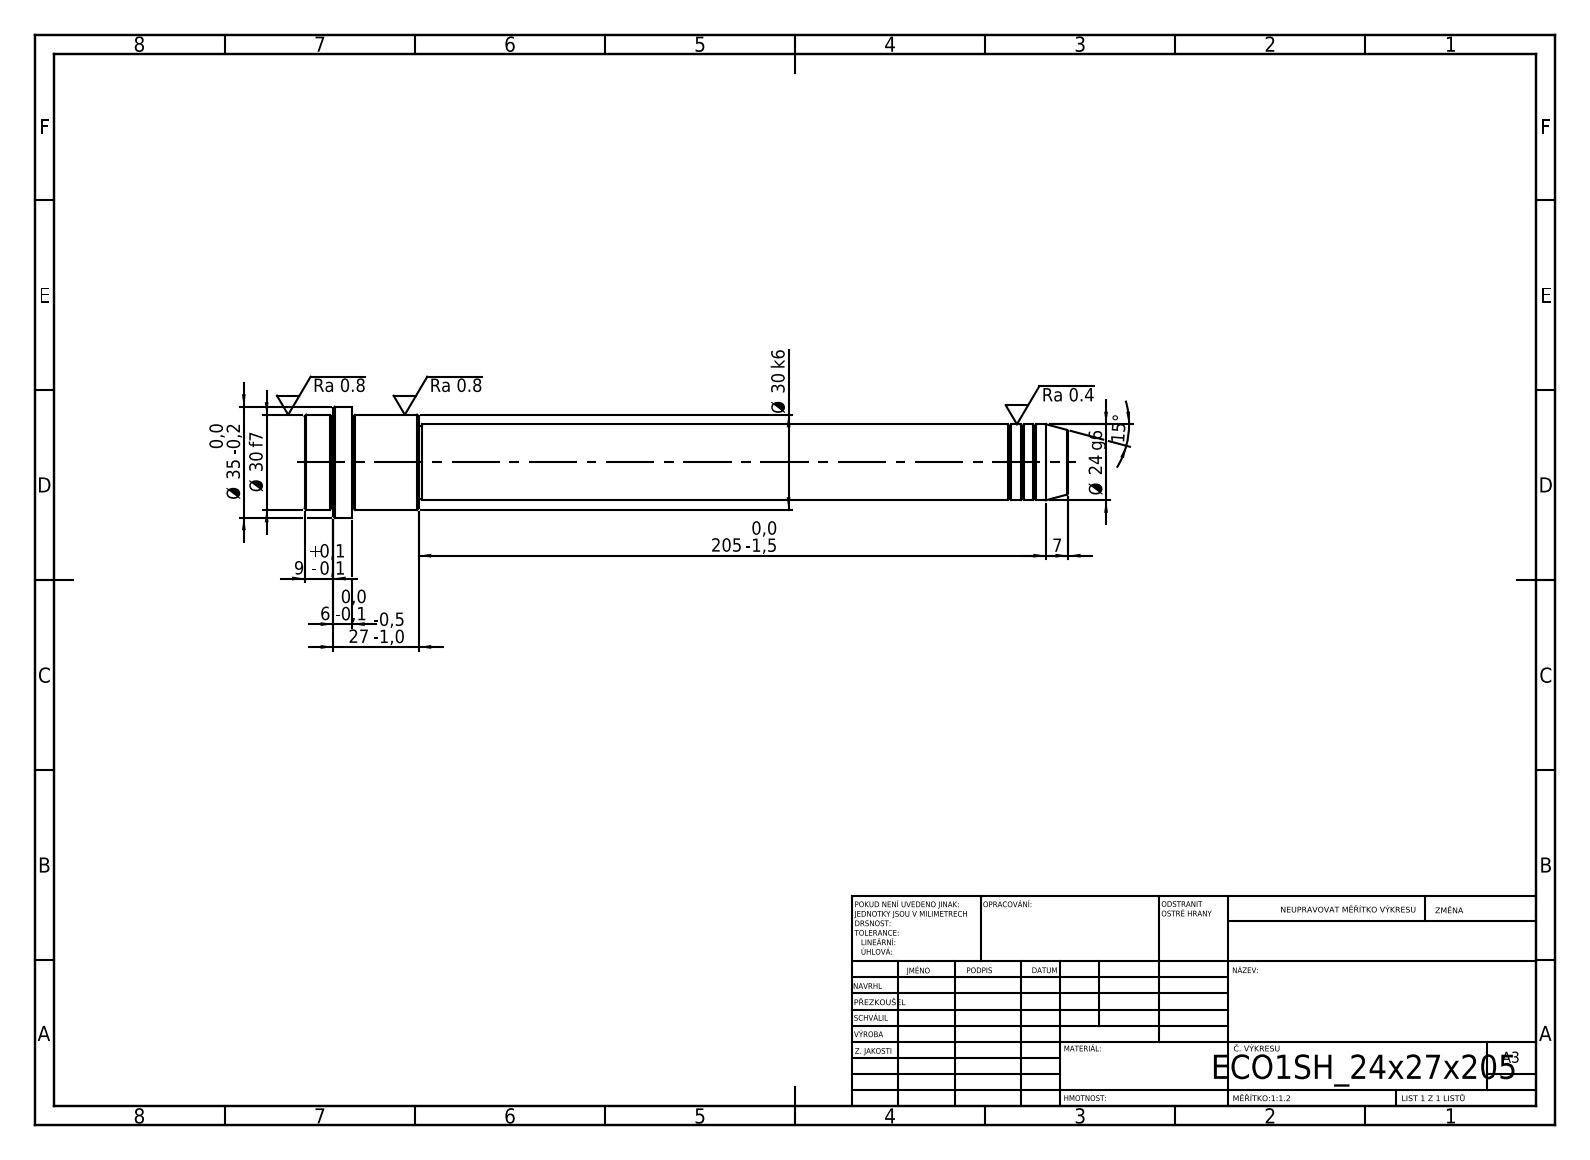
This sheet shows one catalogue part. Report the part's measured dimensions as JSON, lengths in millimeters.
{"step_written_by": "SolidWorks 2019 (CONFIG_CONTROL_DESIGN)", "units": "millimeters", "bodies": {"solids": 1, "faces": 52, "planar": 6, "cylindrical": 16, "other": 30}, "overall_size": [241, 35, 35], "volume_mm3": 119013, "surface_area_mm2": 20910, "round_bosses_or_shafts": [[35, 1], [30, 1], [24, 1], [23, 1]], "face_to_face_distances": [241, 226, 15, 205, 21, 36, 232, 27, 6, 9]}
